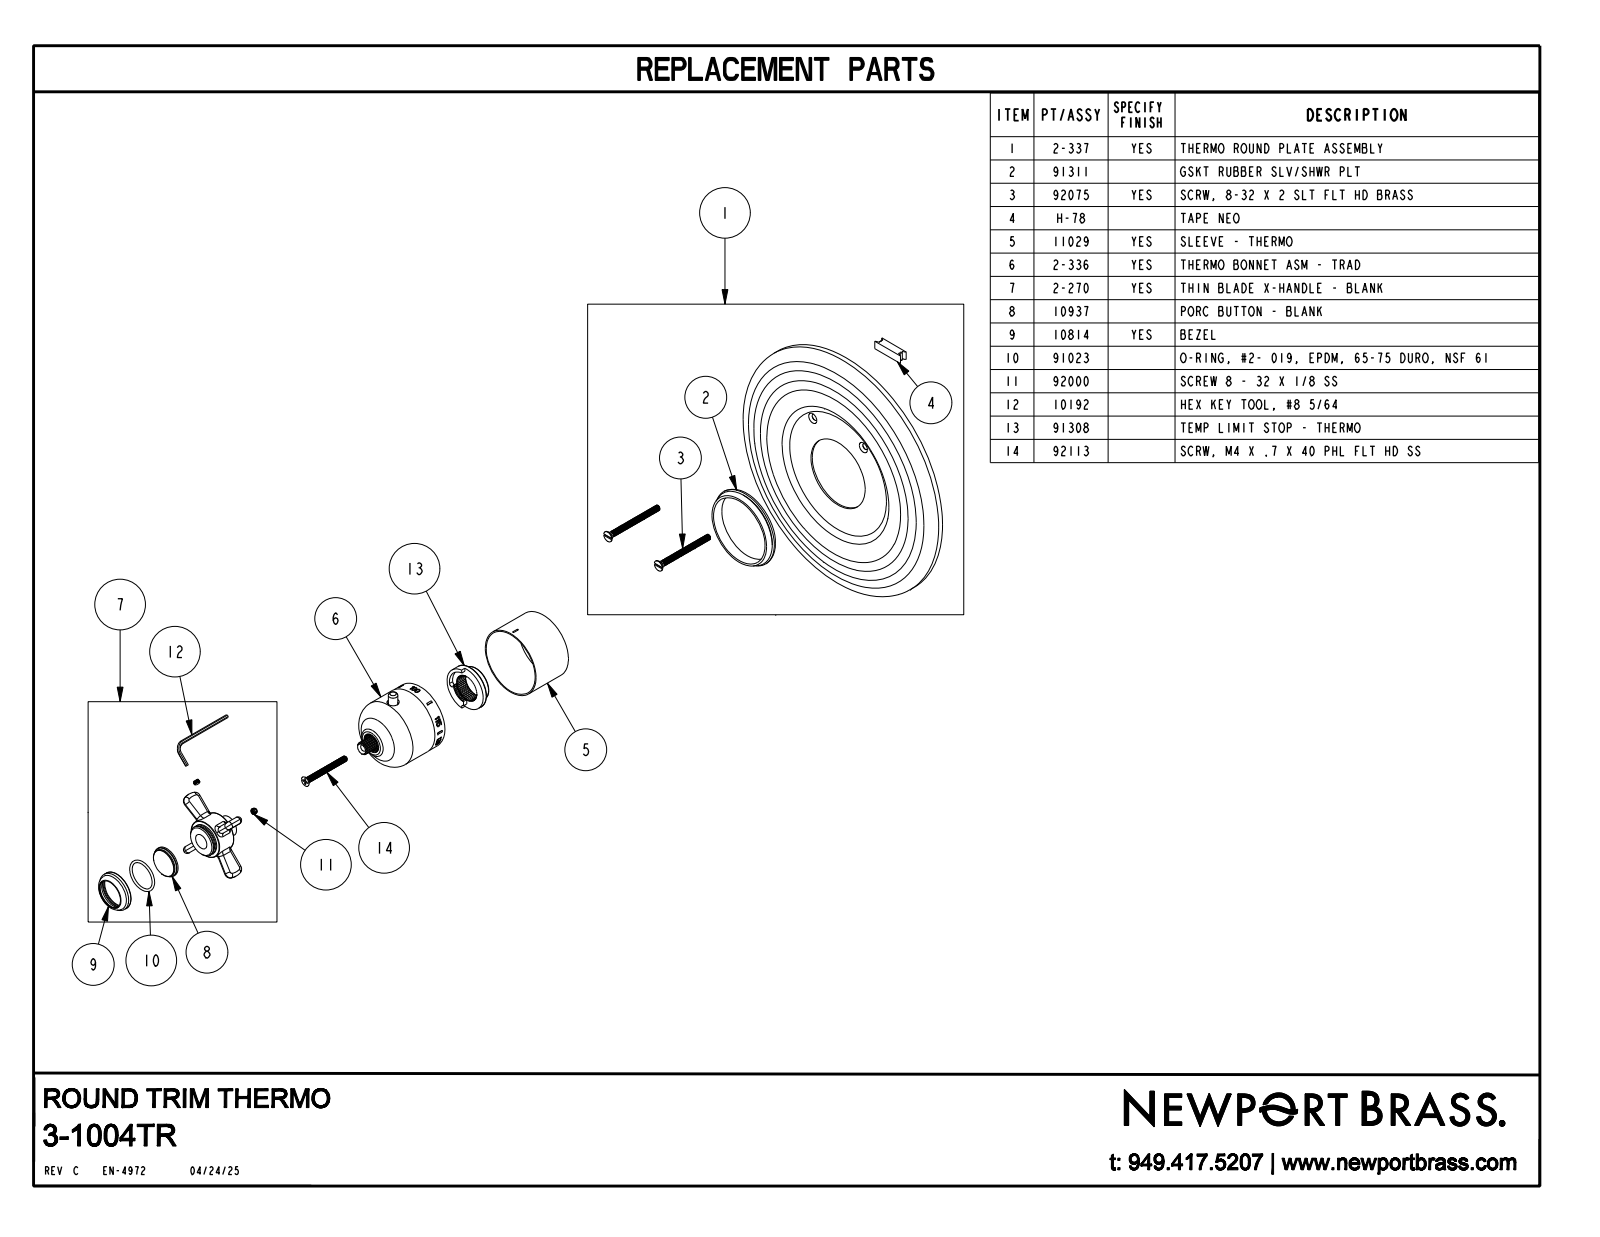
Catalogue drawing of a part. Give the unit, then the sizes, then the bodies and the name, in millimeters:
Units: millimetres
Overall size (bounding box): 190.5 × 190.5 × 104.6
Round holes (diameter × count): ⌀20.7 ×1
Round bosses / shafts (diameter × count): ⌀190.5 ×1, ⌀50 ×1, ⌀49.3 ×1, ⌀49 ×1, ⌀28.3 ×1, ⌀27.9 ×1, ⌀20.3 ×1, ⌀15.3 ×1
Partial cylindrical surfaces — rounded edges, fillets, slot ends (radius × count): R2.5 ×14, R24.6 ×1
Main face-to-face distances: 8, 5.1, 79.5, 71.5, 12, 4, 67.5, 97.7, 89.8, 85.8
Volume: 418 200 mm³ · Surface area: 77 160 mm²
Bodies: 1 solid, 498 faces (339 planar, 59 cylindrical, 100 other)
Part name (STEP PRODUCT): 3-1004TR
STEP written by: CREO PARAMETRIC BY PTC INC, 2018400 (CONFIG_CONTROL_DESIGN)
